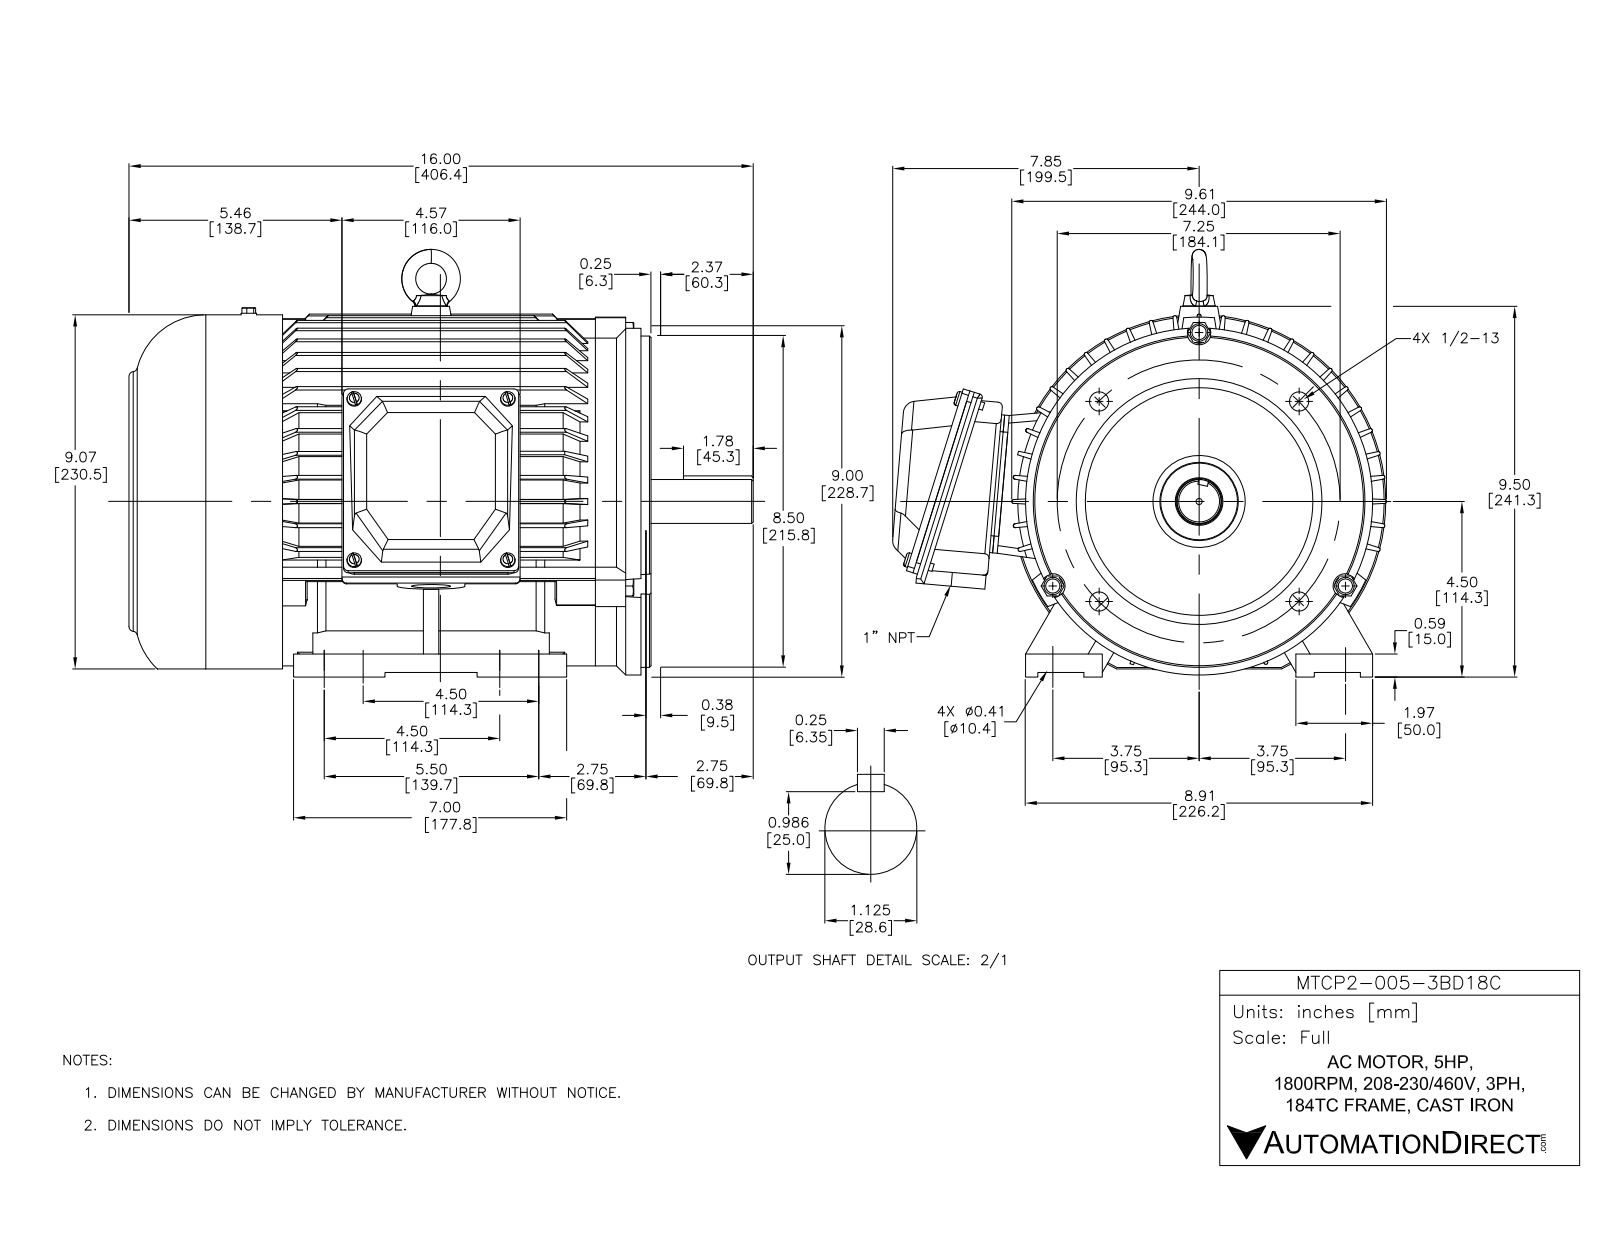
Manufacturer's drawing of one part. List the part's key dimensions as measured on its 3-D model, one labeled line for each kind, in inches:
Part name (STEP PRODUCT): PEWWE-184TC
STEP written by: SolidWorks 2017 (AUTOMOTIVE_DESIGN)
Units: inches
Bodies: 15 solids, 1628 faces (738 planar, 587 cylindrical, 303 other)
Overall size (bounding box): 15.999 × 12.659 × 10.961
Volume: 619.8 in³ · Surface area: 1 349 in²
Round holes (diameter × count): ⌀0.228 ×8, ⌀0.433 ×8, ⌀0.276 ×6, ⌀0.197 ×4, ⌀0.236 ×4, ⌀0.492 ×4, ⌀0.362 ×3, ⌀0.394 ×3, ⌀0.315 ×1, ⌀1 ×1, ⌀1.181 ×1, ⌀1.969 ×1
Round bosses / shafts (diameter × count): ⌀0.315 ×4, ⌀0.197 ×4, ⌀0.283 ×3, ⌀9.567 ×1, ⌀8.894 ×1, ⌀8.5 ×1, ⌀2.362 ×1, ⌀1.496 ×1
Partial cylindrical surfaces — rounded edges, fillets, slot ends (radius × count): R0.02 ×256, R0.118 ×14, R0.049 ×13, R0.059 ×8, R0.157 ×8, R0.276 ×8, R0.315 ×8, R0.091 ×6
Main face-to-face distances: 0.039, 3.432, 0.118, 0.472, 9.85, 13.282, 13.322, 3.471, 0.118, 0.157
Hole centre spacings: 3.937, 2.677, 3.786, 4.331, 5.853, 1, 2.678, 4.33
